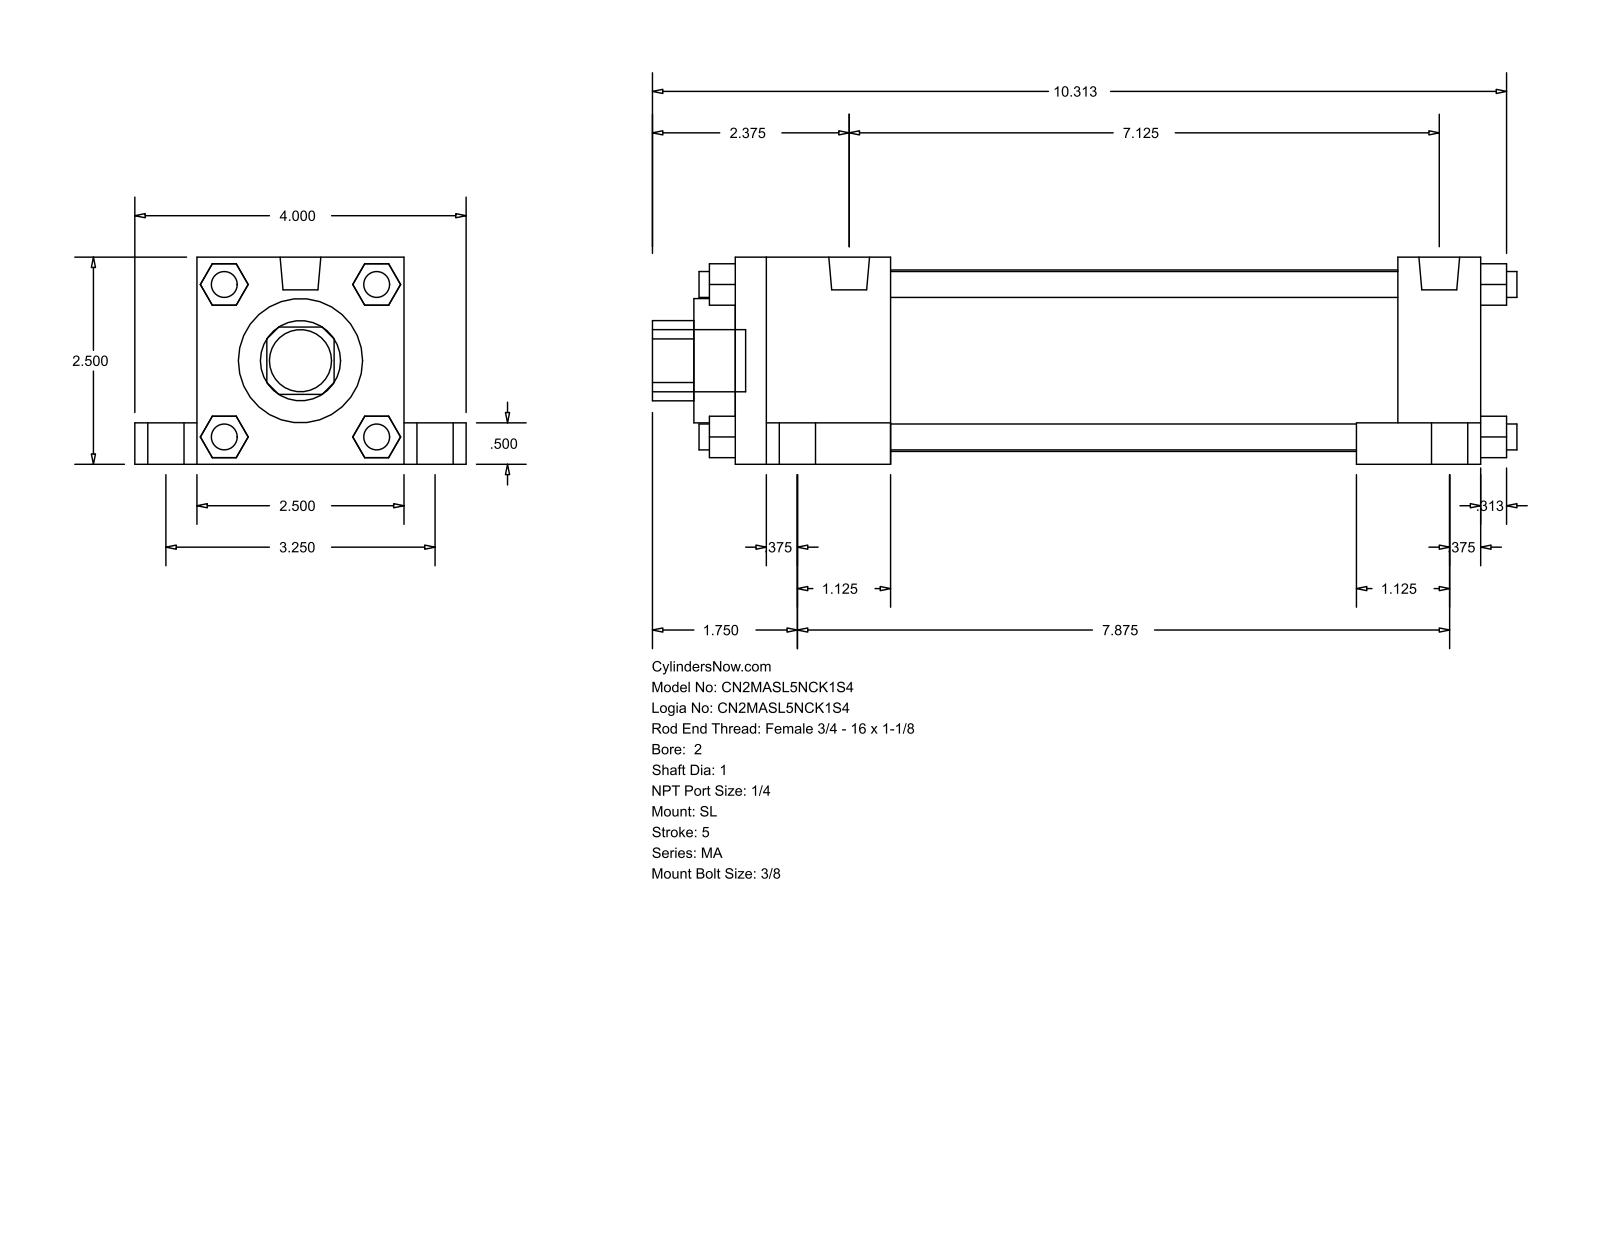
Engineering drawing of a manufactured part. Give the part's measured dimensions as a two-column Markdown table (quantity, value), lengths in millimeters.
| quantity | value |
| --- | --- |
| part name | MA_SL__0200_1 |
| STEP written by | GSSL Pune (CONFIG_CONTROL_DESIGN) |
| units | millimeters |
| bodies | 0 solids, 148 faces (112 planar, 36 cylindrical, 0 other) |
| overall size | 265.11 × 101.6 × 63.5 |
| round holes (diameter × count) | 25.4 × 1, 38.1 × 1, 55.63 × 1 |
| round bosses / shafts (diameter × count) | 7.94 × 8, 17.46 × 4, 11.11 × 4, 12.49 × 2, 19.05 × 1 |
| partial cylindrical surfaces (radius × count) | 12.29 × 1 |
| main face-to-face distances | 63.5, 12.7, 228.6, 19.05, 82.55, 25.4, 50.8, 47.63, 180.97, 203.2 |
